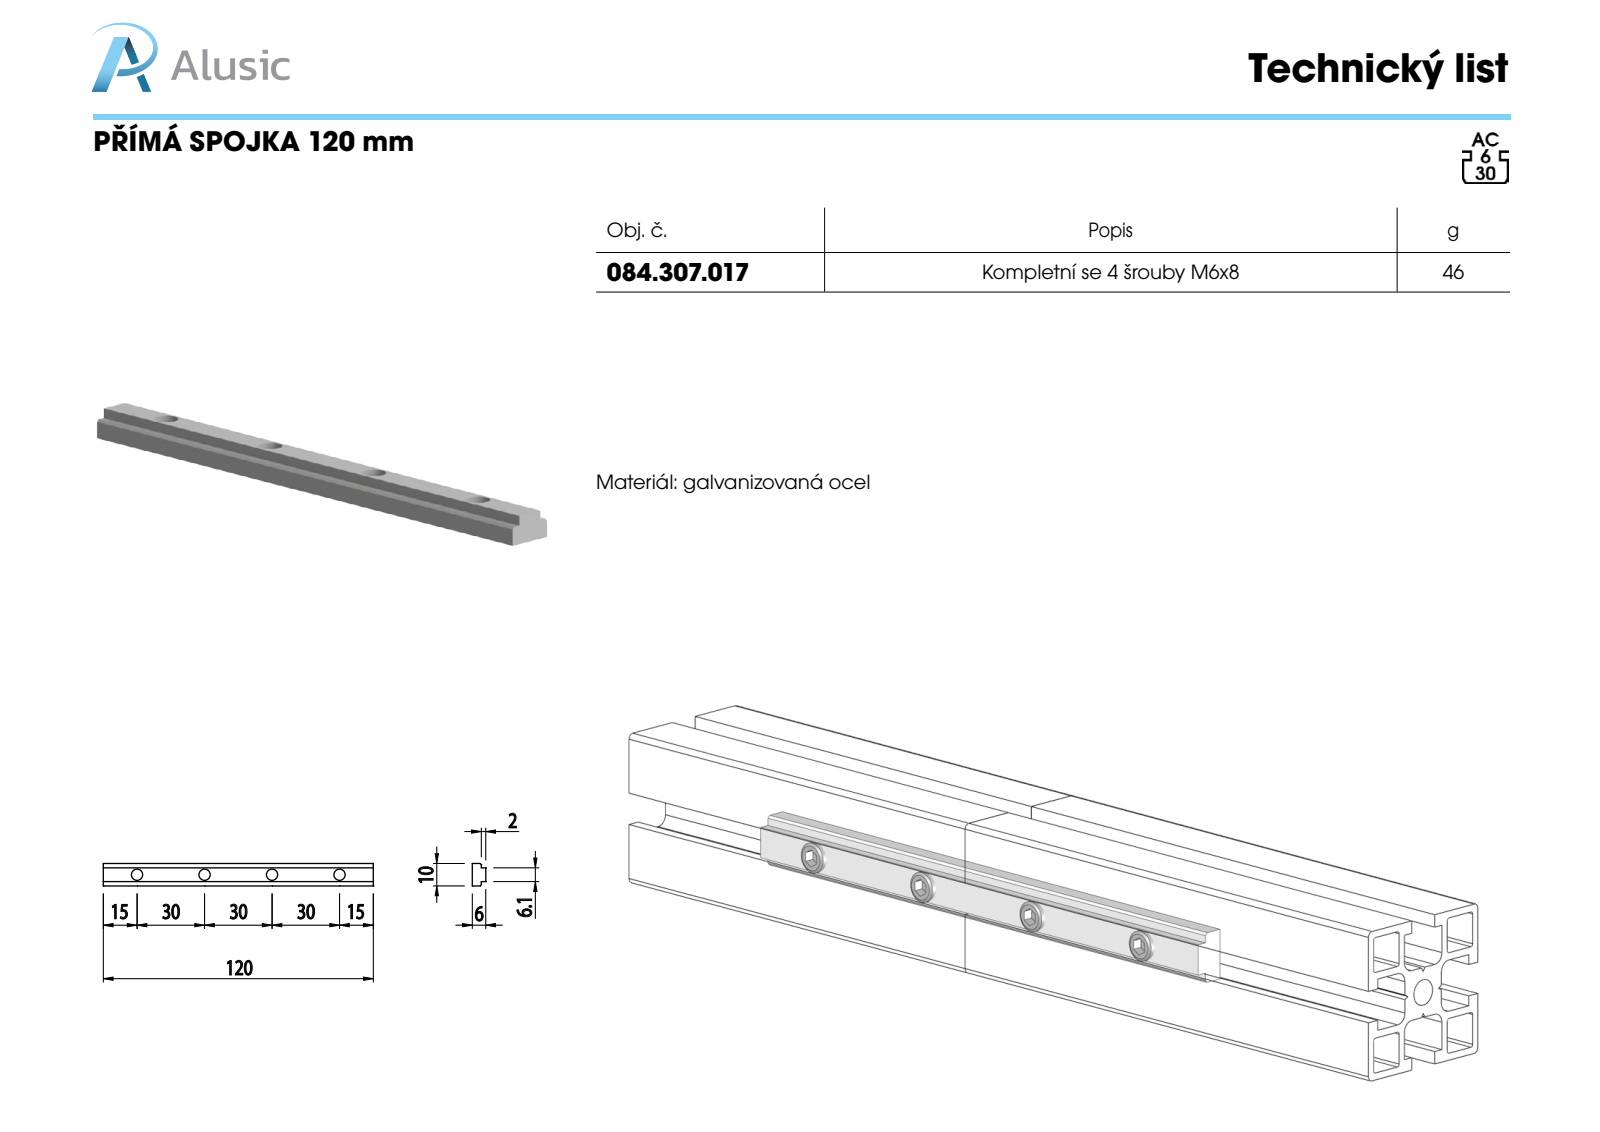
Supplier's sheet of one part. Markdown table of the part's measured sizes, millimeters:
| quantity | value |
| --- | --- |
| part name | 084.307.017 |
| STEP written by | SolidWorks 2011 (CONFIG_CONTROL_DESIGN) |
| units | millimeters |
| bodies | 1 solid, 20 faces (12 planar, 8 cylindrical, 0 other) |
| overall size | 120 × 10 × 6 |
| volume | 5 763 mm³ |
| surface area | 4 094 mm² |
| round holes (diameter × count) | 5 × 4 |
| main face-to-face distances | 6, 1.95, 8.05, 10, 4, 2, 6.1, 120 |
| hole center spacings | 30, 60, 90 |
